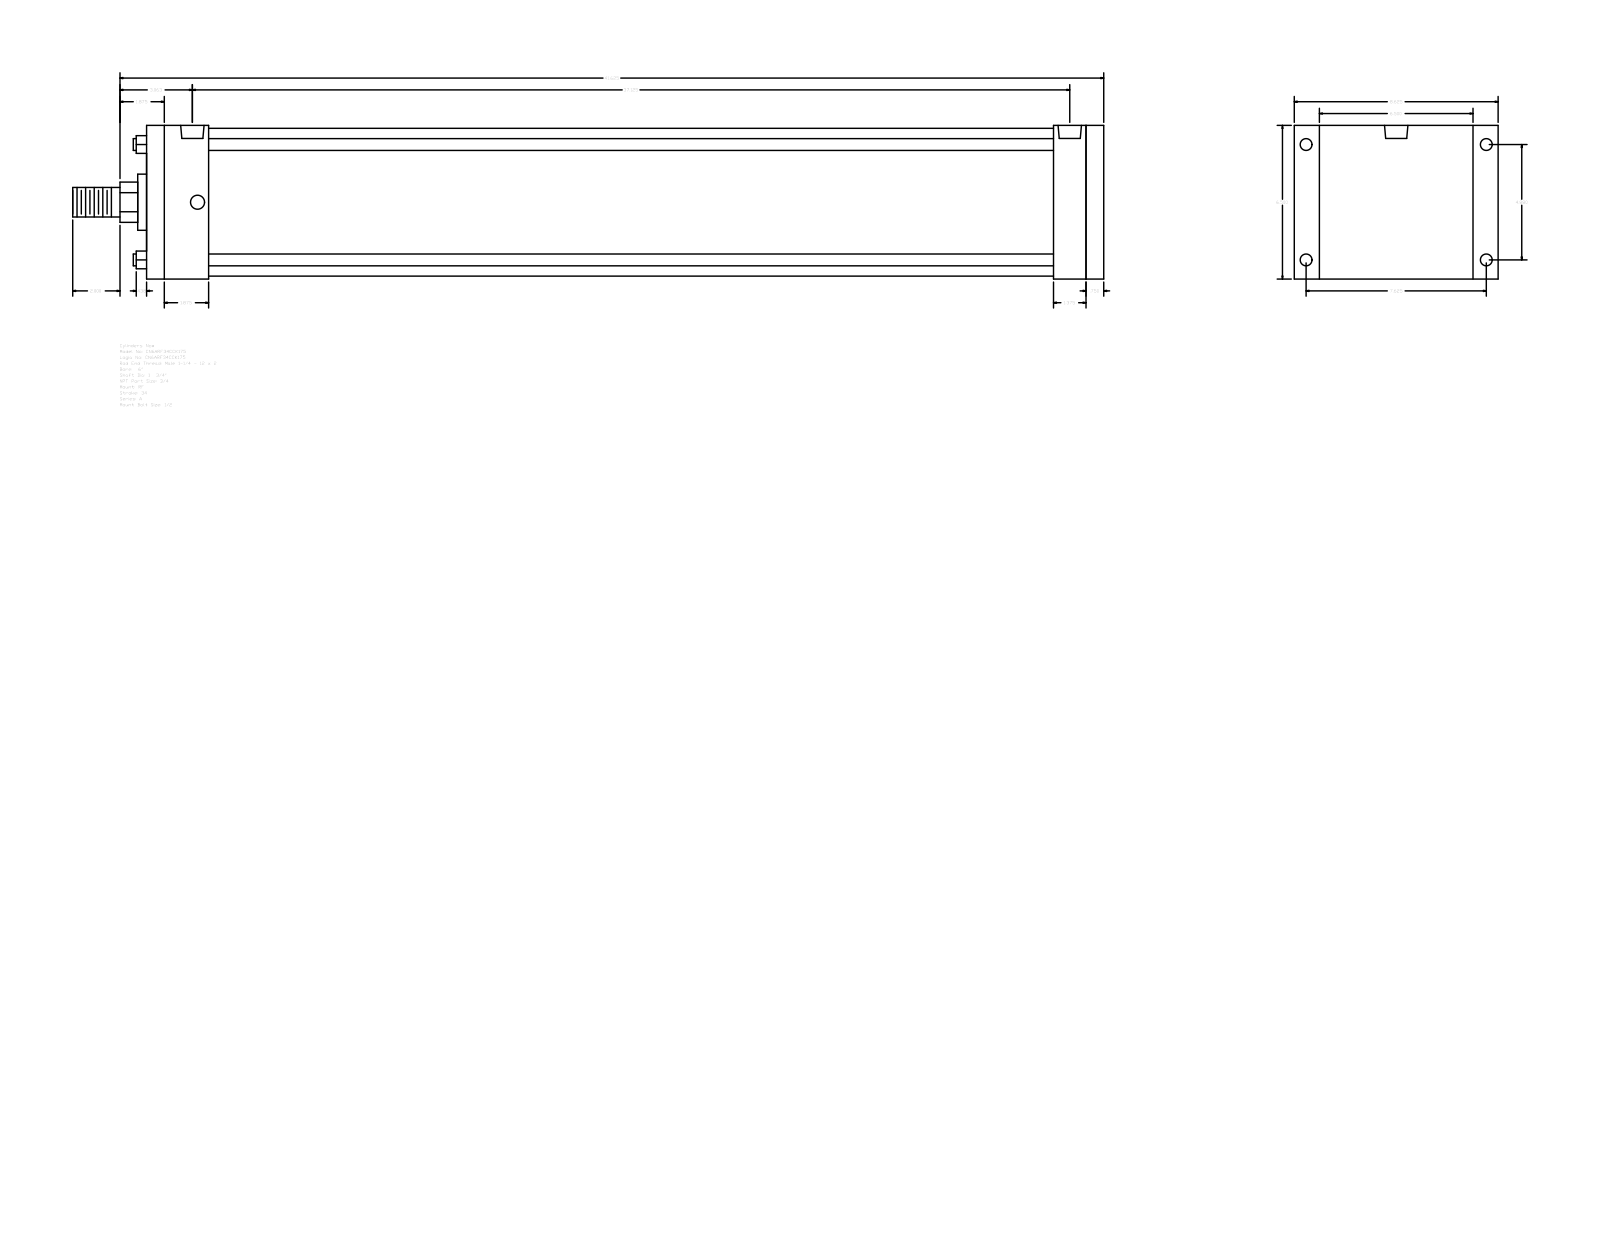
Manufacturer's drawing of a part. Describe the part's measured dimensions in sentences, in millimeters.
The part is named "A_RF__0600_1.75". Its 3-D file was written by "GSSL Pune (CONFIG_CONTROL_DESIGN)". It is 0 solids with 92 faces: 64 planar, 28 cylindrical and 0 other. Overall it measures 1108.08 by 219.07 by 165.1 millimeters. Round holes: 4 of diameter 12.7, 4 of diameter 15.08, 2 of diameter 25.12. Round bosses or shafts: 4 of diameter 12.7, 1 of diameter 158.75, 1 of diameter 60.33, 1 of diameter 44.45, 1 of diameter 31.75. Partial cylindrical surfaces (rounded edges, fillets, slot ends): 1 of radius 21.63. The main face-to-face distances are 165.1, 1028.71, 1009.65, 19.06, 66.68, 942.97, 962.03, 974.73, 908.05, 34.92. The hole center spacings are 5.56, 123.96, 193.68, 229.95, 931.85, 937.41, 942.97.
